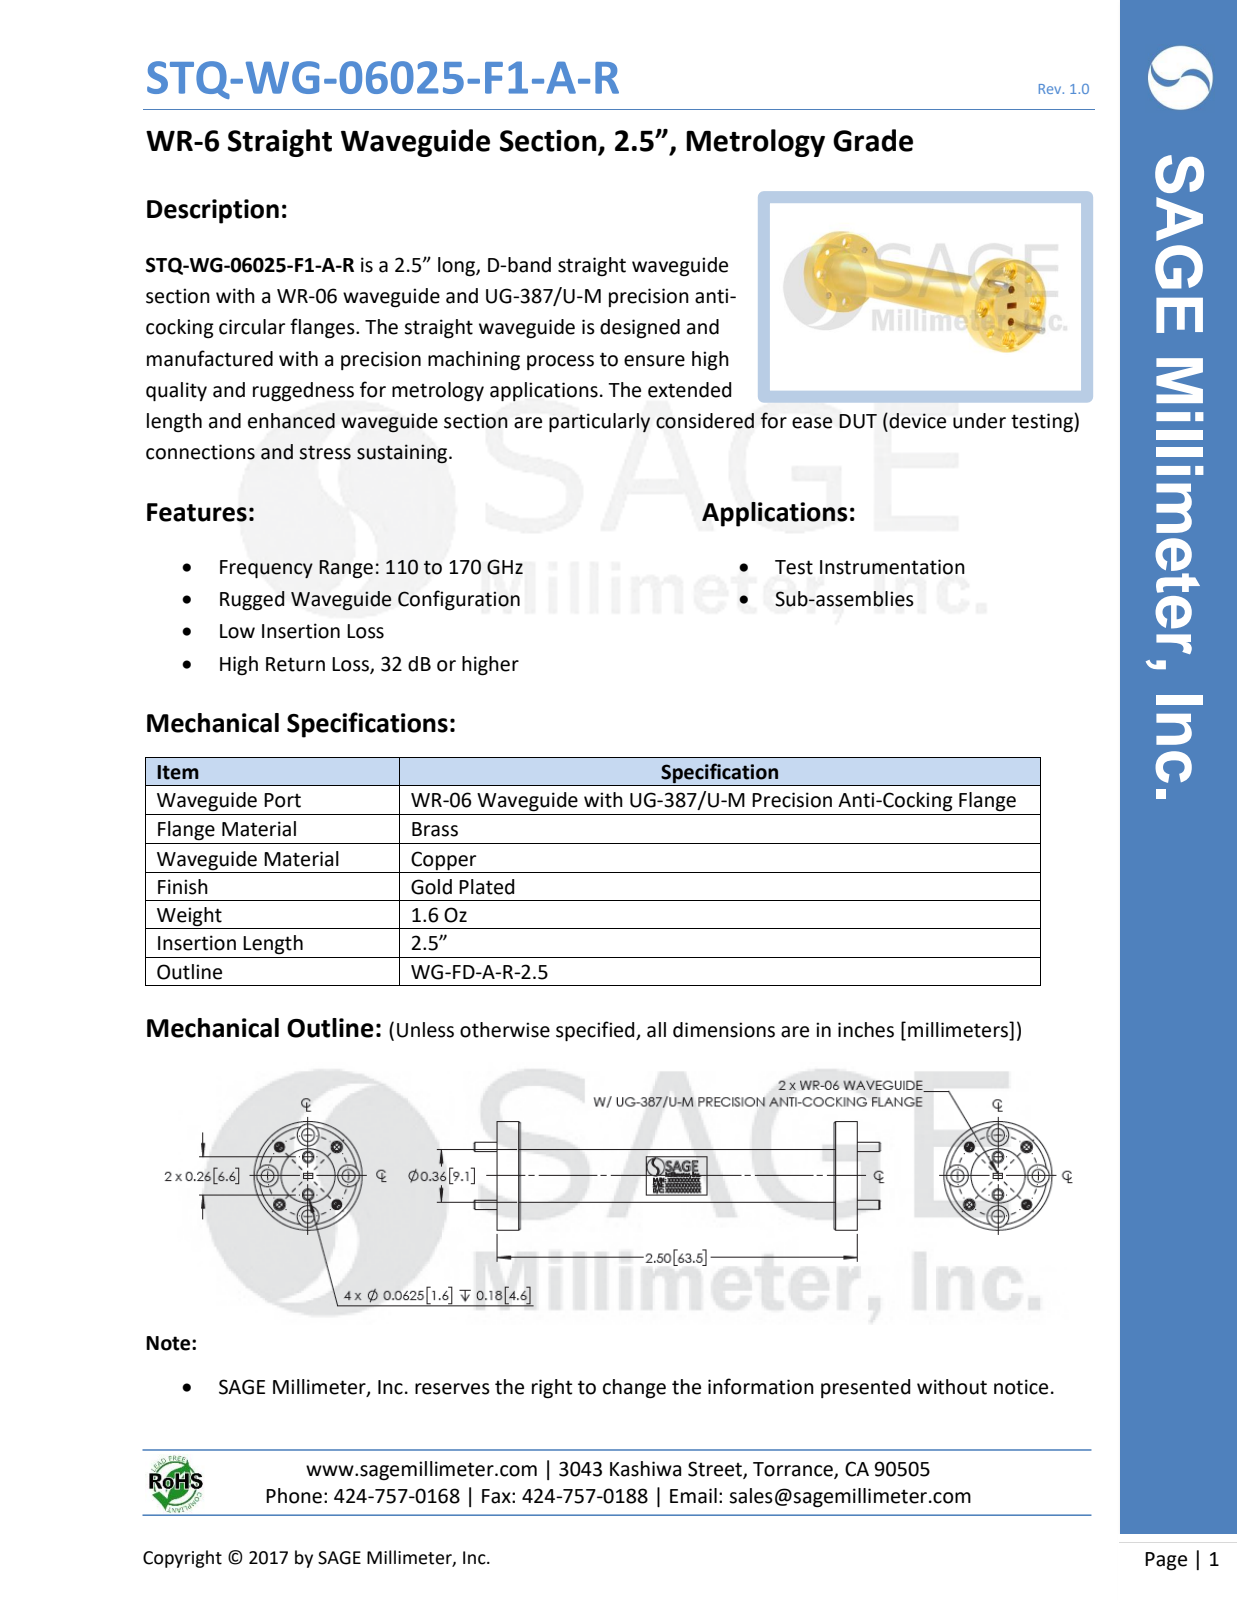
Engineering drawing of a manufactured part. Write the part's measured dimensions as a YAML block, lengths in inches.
part_name: "DEFEATURED STQ-WG-06025-F1-A-R"
step_written_by: "SolidWorks 2020 (CONFIG_CONTROL_DESIGN)"
units: inches
bodies: {solids: 5, faces: 168, planar: 34, cylindrical: 82, other: 52}
overall_size: [2.82, 0.75, 0.75]
volume: 0.341
surface_area: 5.729
round_holes:
  - {diameter: 0.061, count: 4}
  - {diameter: 0.067, count: 4}
  - {diameter: 0.089, count: 4}
  - {diameter: 0.14, count: 4}
  - {diameter: 0.063, count: 2}
  - {diameter: 0.68, count: 1}
round_bosses_or_shafts:
  - {diameter: 0.063, count: 4}
  - {diameter: 0.75, count: 1}
  - {diameter: 0.375, count: 1}
  - {diameter: 0.36, count: 1}
face_to_face_distances: [0.16, 0.14, 2.32, 0.02, 2.34, 2.48, 2.18, 2.5, 2.46, 0.06]
hole_center_spacings: [0.215, 0.281, 0.398, 0.519, 0.21, 0.31, 0.384, 0.562]
